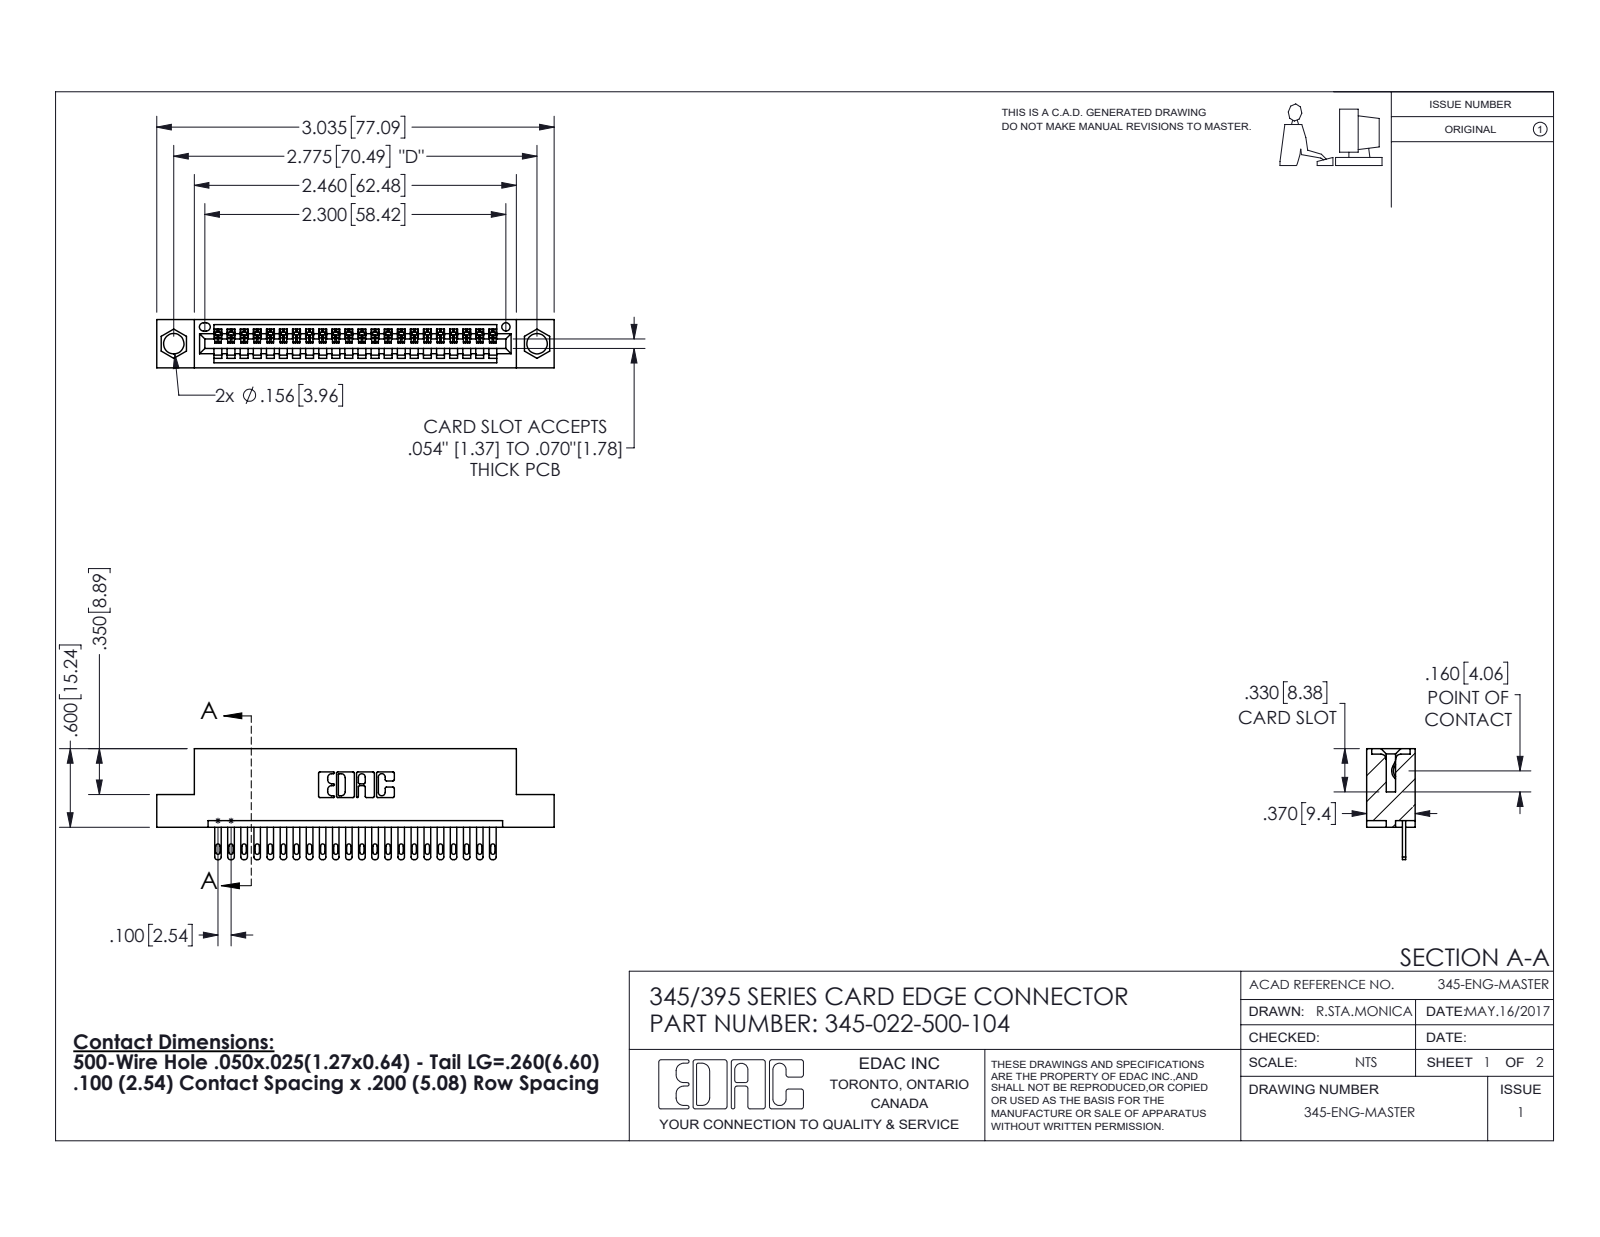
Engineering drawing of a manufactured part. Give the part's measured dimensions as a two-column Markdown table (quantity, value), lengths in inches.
| quantity | value |
| --- | --- |
| part name | 345 Part_Flush Mounting Lugs - 0.156 Dia-TH; 345-022-500-104; 345-292-001_345-293-100 |
| STEP written by | SolidWorks 2016 (CONFIG_CONTROL_DESIGN) |
| units | inches |
| bodies | 23 solids, 1314 faces (828 planar, 486 cylindrical, 0 other) |
| overall size | 3.035 × 0.847 × 0.37 |
| volume | 0.432 in³ |
| surface area | 13.95 in² |
| round holes (diameter × count) | 0.156 × 2, 0.064 × 1 |
| partial cylindrical surfaces (radius × count) | 0.006 × 44, 0.016 × 44, 0.02 × 44, 0.01 × 22, 0.007 × 6, 0.031 × 6, 0.026 × 3, 0.031 × 2 |
| main face-to-face distances | 0.298, 0.072, 0.2, 0.37, 0.098, 0.272, 0.025, 0.225, 0.149, 0.072 |
| hole center spacings | 0.27, 2.541, 2.775 |
